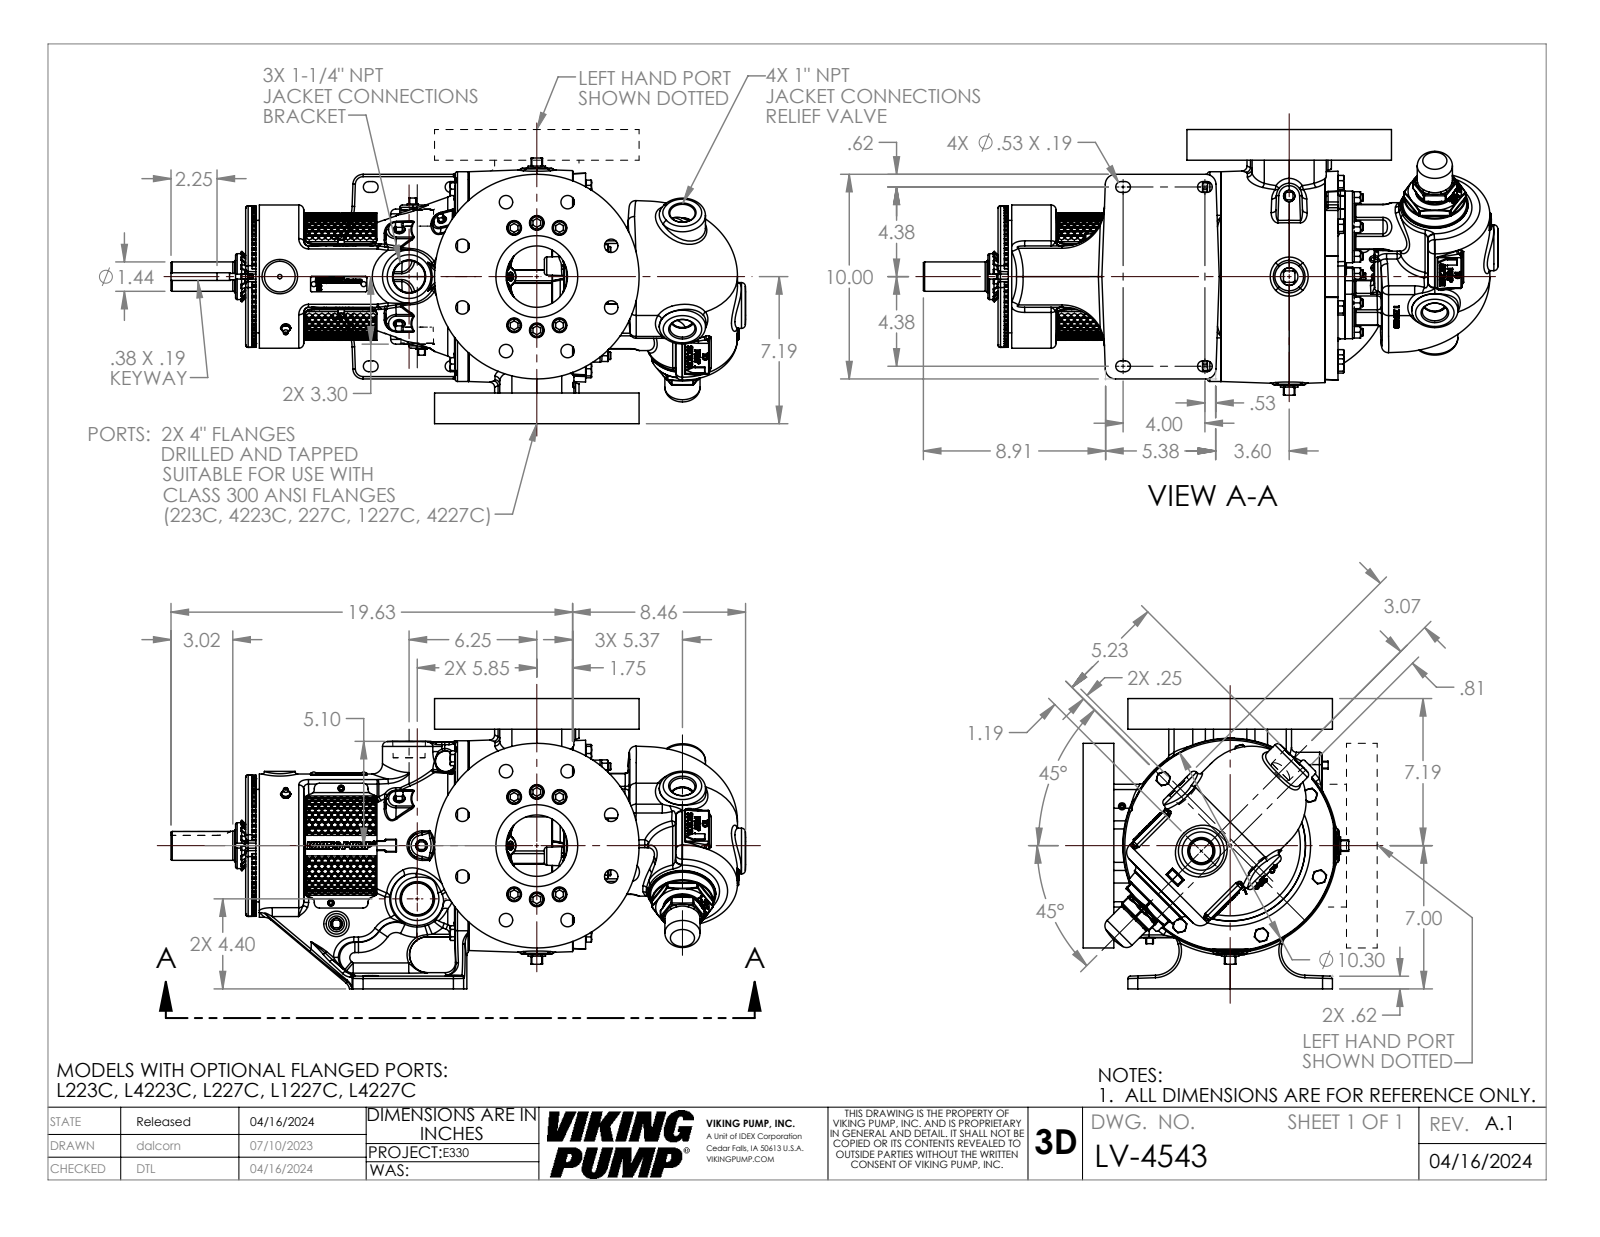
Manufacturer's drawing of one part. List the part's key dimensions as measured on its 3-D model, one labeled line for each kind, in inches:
Part name (STEP PRODUCT): LV-4543
STEP written by: SolidWorks 2024 (AUTOMOTIVE_DESIGN)
Units: inches
Bodies: 1 solid, 5646 faces (1862 planar, 1017 cylindrical, 2767 other)
Overall size (bounding box): 28.059 × 14.188 × 13.053
Volume: 1 328 in³ · Surface area: 1 825 in²
Round holes (diameter × count): ⌀0.656 ×16, ⌀0.469 ×12, ⌀0.719 ×12, ⌀1.094 ×8, ⌀0.199 ×6, ⌀0.25 ×6, ⌀0.159 ×3, ⌀0.266 ×2, ⌀0.313 ×2, ⌀3 ×2, ⌀0.453 ×1, ⌀1.577 ×1
Round bosses / shafts (diameter × count): ⌀0.437 ×15, ⌀0.66 ×12, ⌀0.625 ×9, ⌀0.369 ×8, ⌀0.625 ×6, ⌀3.5 ×3, ⌀0.312 ×3, ⌀10 ×2
Partial cylindrical surfaces — rounded edges, fillets, slot ends (radius × count): R0.063 ×109, R0.12 ×82, R0.069 ×74, R0.03 ×34, R0.5 ×34, R0.24 ×16, R1 ×16, R0.19 ×14
Main face-to-face distances: 1.5, 12.687, 14.187, 2.25, 13.792, 3.537, 10.255, 2.75, 0.5, 2.143
Hole centre spacings: 7.276, 3, 3.937, 1.375, 2.625, 1.136, 2.18, 2.675
